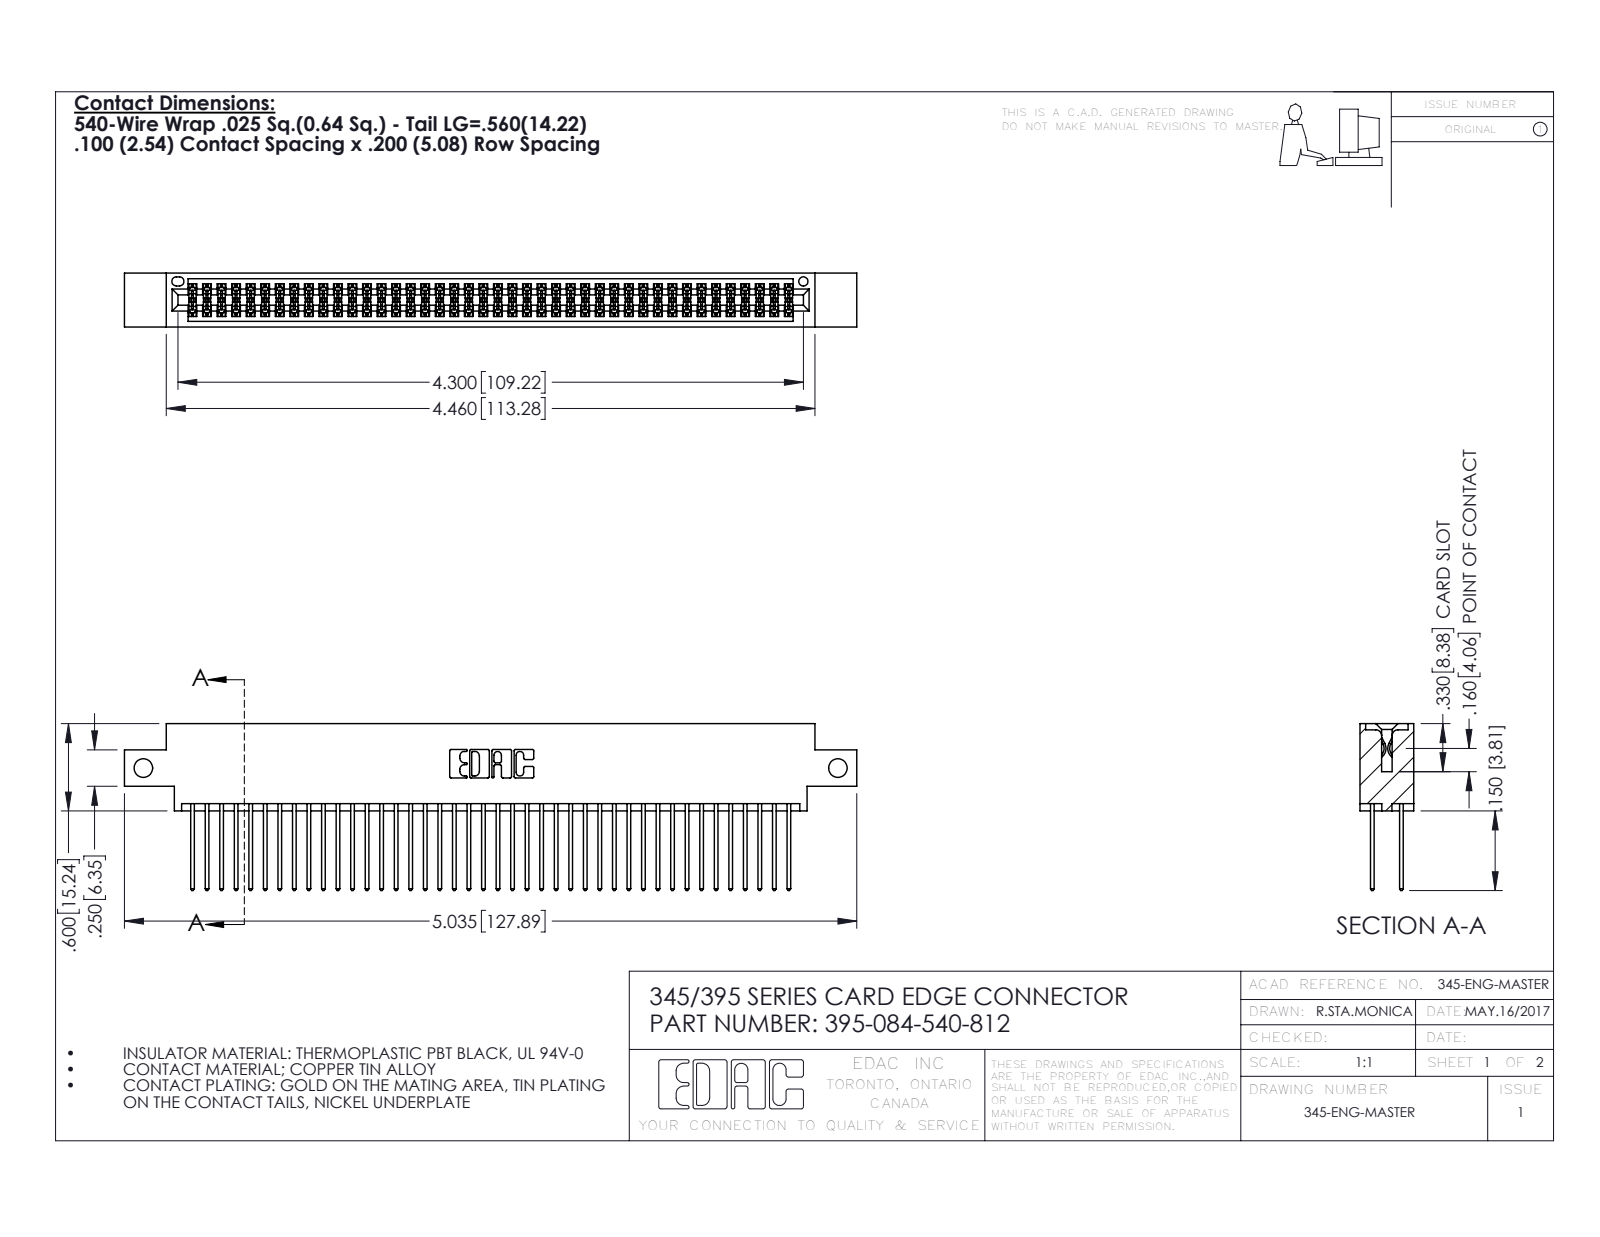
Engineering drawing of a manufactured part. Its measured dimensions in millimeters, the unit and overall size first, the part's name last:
Units: millimetres
Overall size (bounding box): 127.9 × 29.1 × 9.4
Round holes (diameter × count): ⌀3.3 ×2, ⌀1.6 ×1
Partial cylindrical surfaces — rounded edges, fillets, slot ends (radius × count): R0.2 ×126, R0.3 ×84, R0.3 ×22, R0.2 ×6, R0.8 ×6, R0.7 ×3, R0.4 ×2, R0.5 ×2
Main face-to-face distances: 7.6, 1.8, 5.1, 2.5, 6.9, 0.6, 9.4, 5.7, 4.4, 3.8
Hole centre spacings: 121.3
Volume: 12 500 mm³ · Surface area: 20 030 mm²
Bodies: 85 solids, 4330 faces (2856 planar, 1474 cylindrical, 0 other)
Part name (STEP PRODUCT): 345 Part_0.170 Offset - Side Mount; 345-292-001_345-293-140; 395-084-540-812
STEP written by: SolidWorks 2016 (CONFIG_CONTROL_DESIGN)
